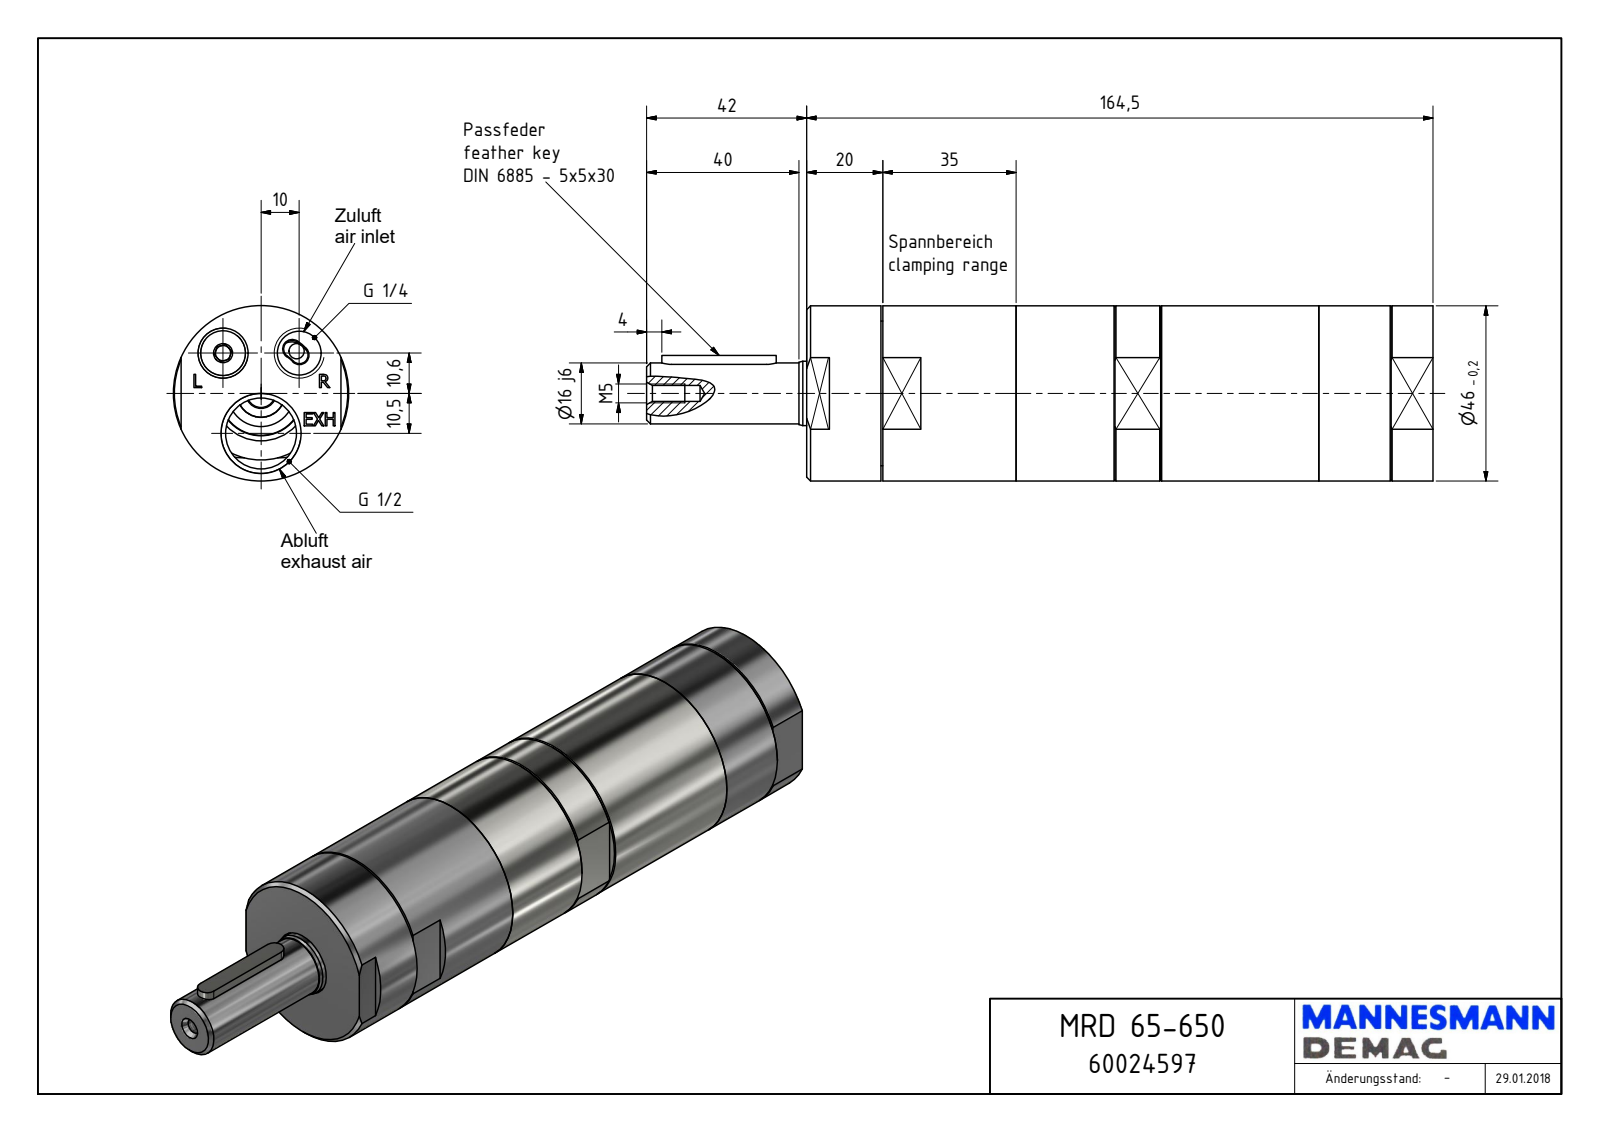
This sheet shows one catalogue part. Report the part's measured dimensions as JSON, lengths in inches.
{"part_name": "MRD 65-650_60024597", "step_written_by": "Autodesk Inventor 2018 (AUTOMOTIVE_DESIGN)", "units": "inches", "bodies": {"solids": 1, "faces": 179, "planar": 118, "cylindrical": 32, "other": 29}, "overall_size": [8.13, 1.811, 1.811], "volume_in3": 16.83, "surface_area_in2": 51.1, "round_holes": [[0.157, 1], [0.163, 1], [0.451, 1], [0.689, 1], [0.733, 1], [1.496, 1], [1.511, 1]], "round_bosses_or_shafts": [[1.811, 1], [1.311, 1], [0.667, 1], [0.63, 1]], "partial_cylinders_radius": [[0.098, 2], [0.197, 2], [0.225, 1], [0.709, 1]], "face_to_face_distances": [6.476, 1.654, 0.787, 5.689, 0.768, 0.02, 5.709, 6.18, 5.412, 5.392], "hole_center_spacings": [0.574, 0.919, 0.413, 0.787]}
